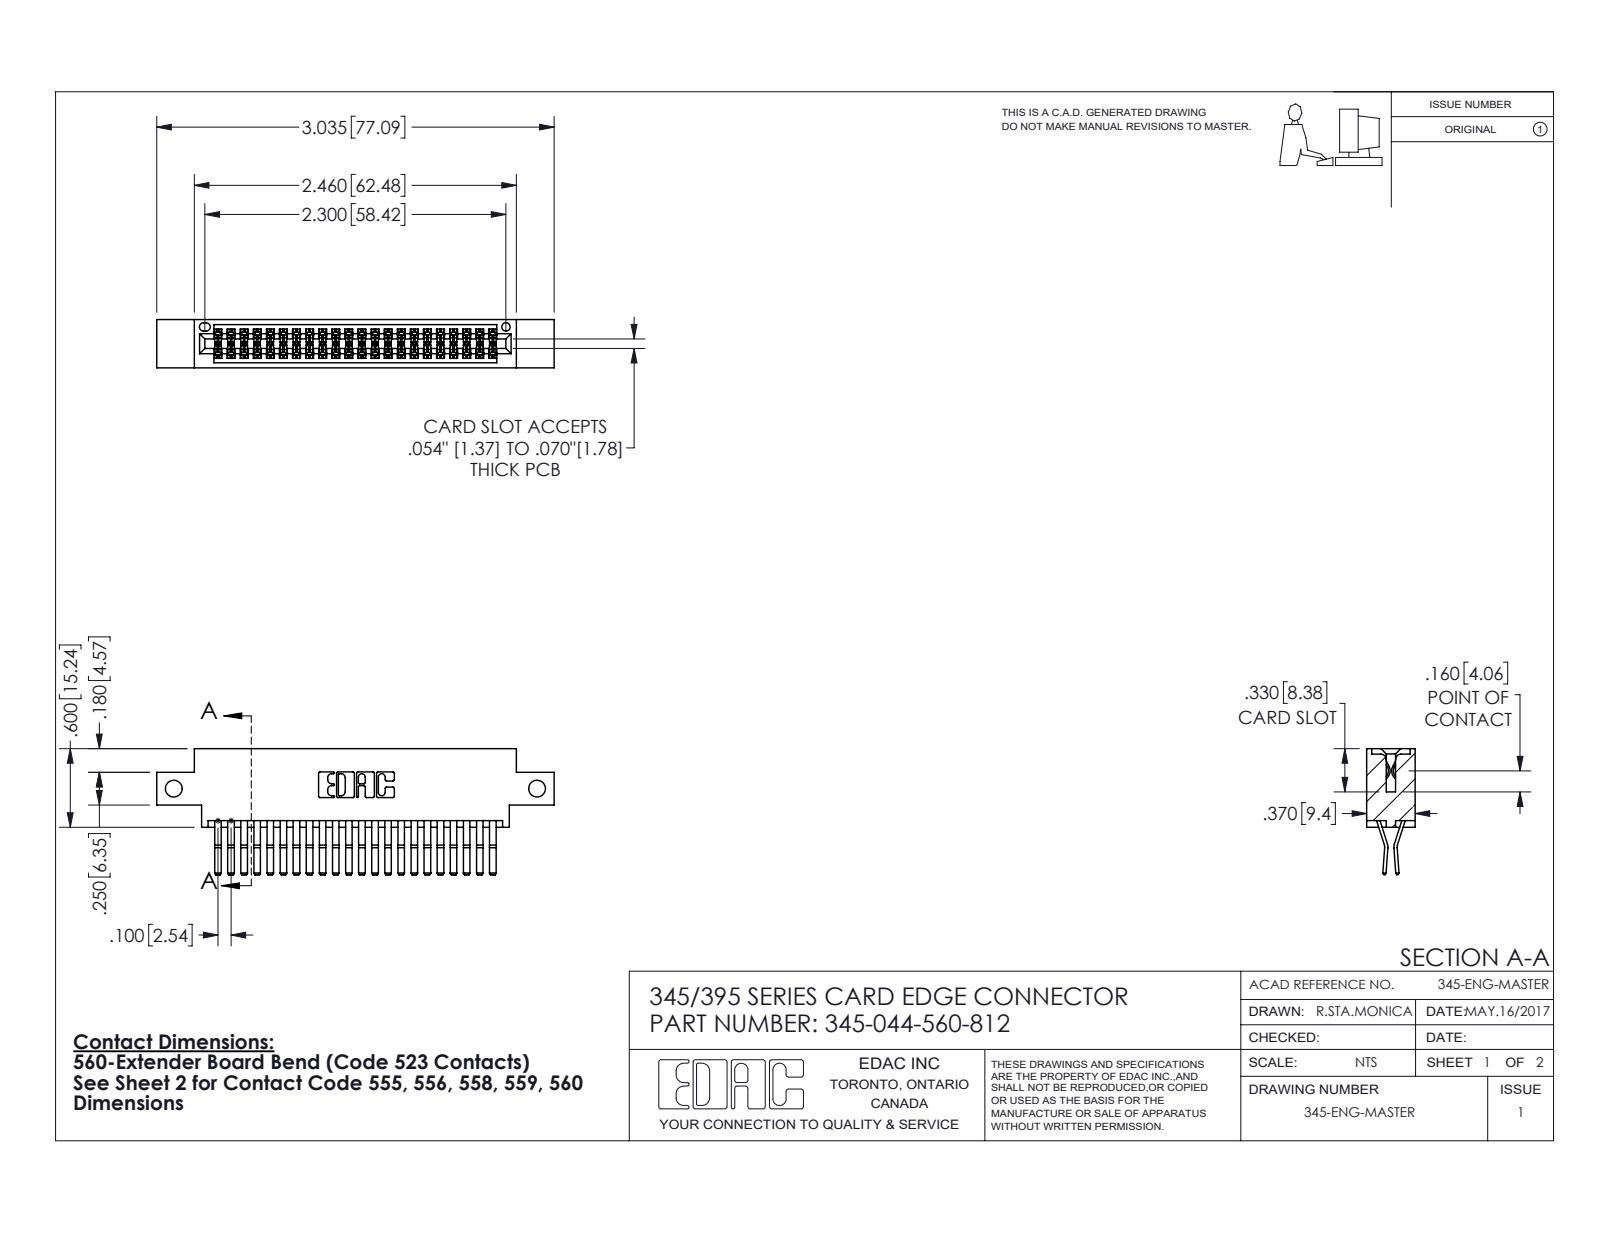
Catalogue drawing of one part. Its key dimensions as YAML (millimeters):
part_name: "345 Part_0.170 Offset - Side Mount; 345-044-560-812; 345-292-001_560 Tail"
step_written_by: "SolidWorks 2016 (CONFIG_CONTROL_DESIGN)"
units: millimeters
bodies: {solids: 45, faces: 2418, planar: 1536, cylindrical: 882, other: 0}
overall_size: [77.1, 24.4, 9.4]
volume: 7390
surface_area: 11280
round_holes:
  - {diameter: 3.3, count: 2}
  - {diameter: 1.6, count: 1}
partial_cylinders:
  - {radius: 0.2, count: 66}
  - {radius: 0.3, count: 22}
  - {radius: 0.2, count: 6}
  - {radius: 0.8, count: 6}
  - {radius: 0.7, count: 3}
  - {radius: 0.3, count: 2}
  - {radius: 0.4, count: 2}
  - {radius: 0.5, count: 2}
face_to_face_distances: [0.6, 7.6, 1.8, 9.4, 5.1, 2.5, 6.9, 5.7, 4.4, 3.8]
hole_center_spacings: [70.5]
